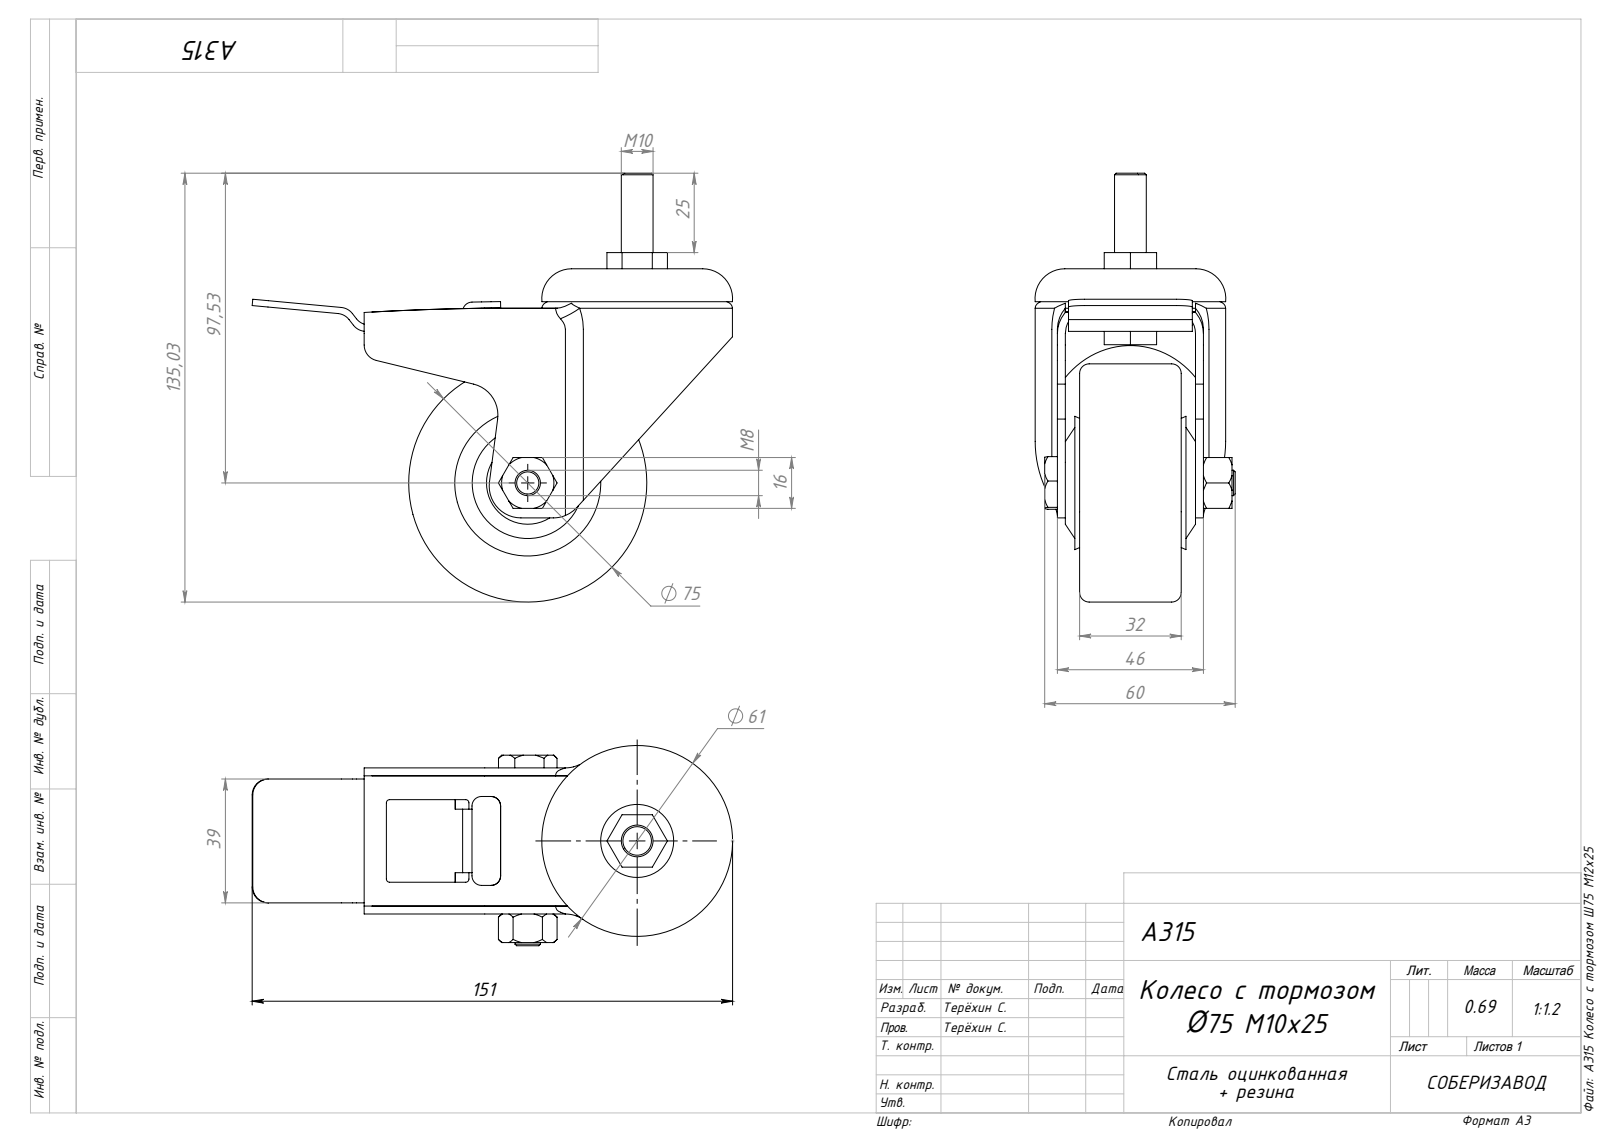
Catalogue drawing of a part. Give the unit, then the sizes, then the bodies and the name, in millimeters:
Units: millimetres
Overall size (bounding box): 151.33 × 135.03 × 63.05
Round holes (diameter × count): ⌀10 ×2, ⌀6 ×1, ⌀8 ×1, ⌀34 ×1
Round bosses / shafts (diameter × count): ⌀75 ×1, ⌀38 ×1
Partial cylindrical surfaces — rounded edges, fillets, slot ends (radius × count): R5 ×7, R10 ×7, R3 ×5, R1 ×4, R2 ×2, R27.5 ×1, R30 ×1, R804.01 ×1
Main face-to-face distances: 4.5, 39, 2.5, 36.5, 7, 43.5, 2, 41, 26, 32
Volume: 195 648 mm³ · Surface area: 80 520 mm²
Bodies: 12 solids, 378 faces (181 planar, 71 cylindrical, 126 other)
Part name (STEP PRODUCT): A315 Болт_00; Основание_00; Защита_00; Болт_00 (+6 more)
STEP written by: SolidWorks 2026 (AUTOMOTIVE_DESIGN)
